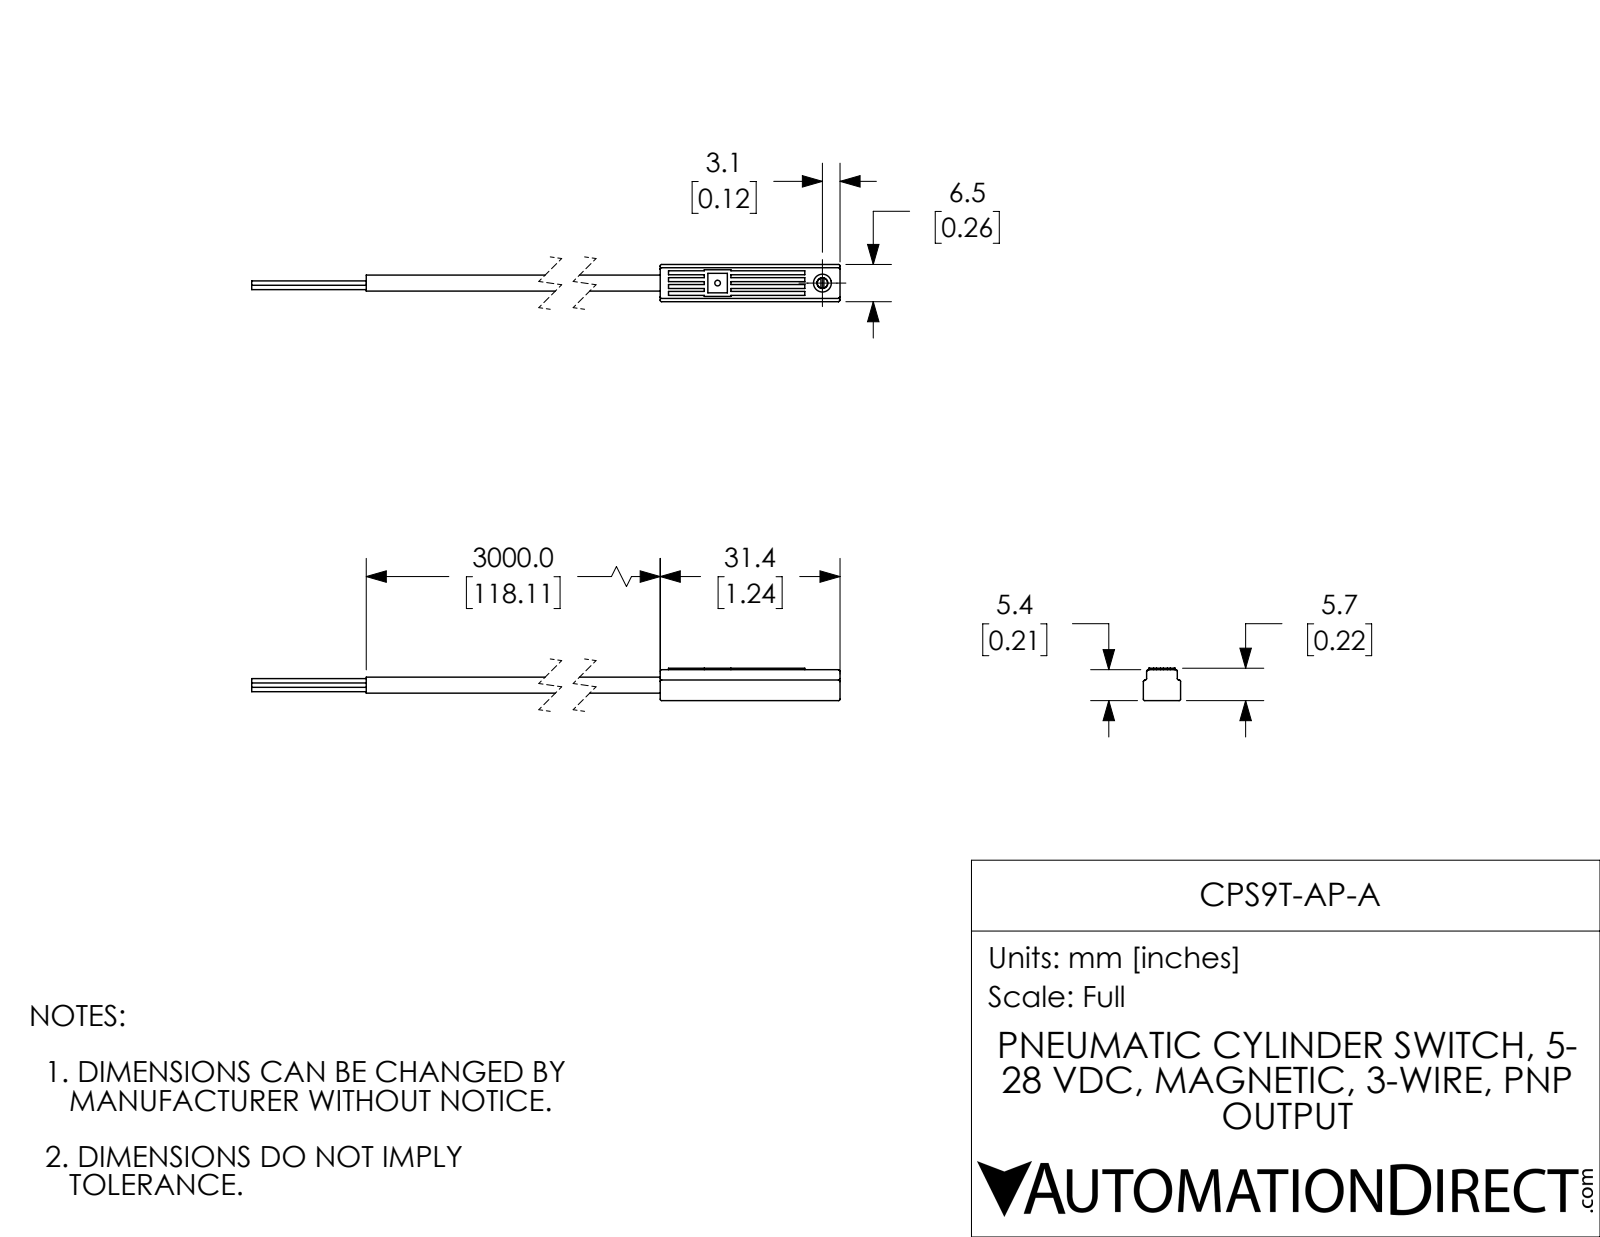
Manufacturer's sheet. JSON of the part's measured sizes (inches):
{"part_name": "CPS9T-AP-A", "step_written_by": "SolidWorks 2017 (AUTOMOTIVE_DESIGN)", "units": "inches", "bodies": {"solids": 2, "faces": 127, "planar": 61, "cylindrical": 34, "other": 32}, "overall_size": [5.826, 0.256, 0.223], "volume_in3": 0.107, "surface_area_in2": 2.968, "round_holes": [[0.075, 1], [0.123, 1]], "round_bosses_or_shafts": [[0.11, 1], [0.071, 1]], "partial_cylinders_radius": [[0.01, 22]], "face_to_face_distances": [0.256, 0.022, 0.233, 0.213, 0.222, 0.211, 0.047, 1.236, 0.094, 0.028]}
